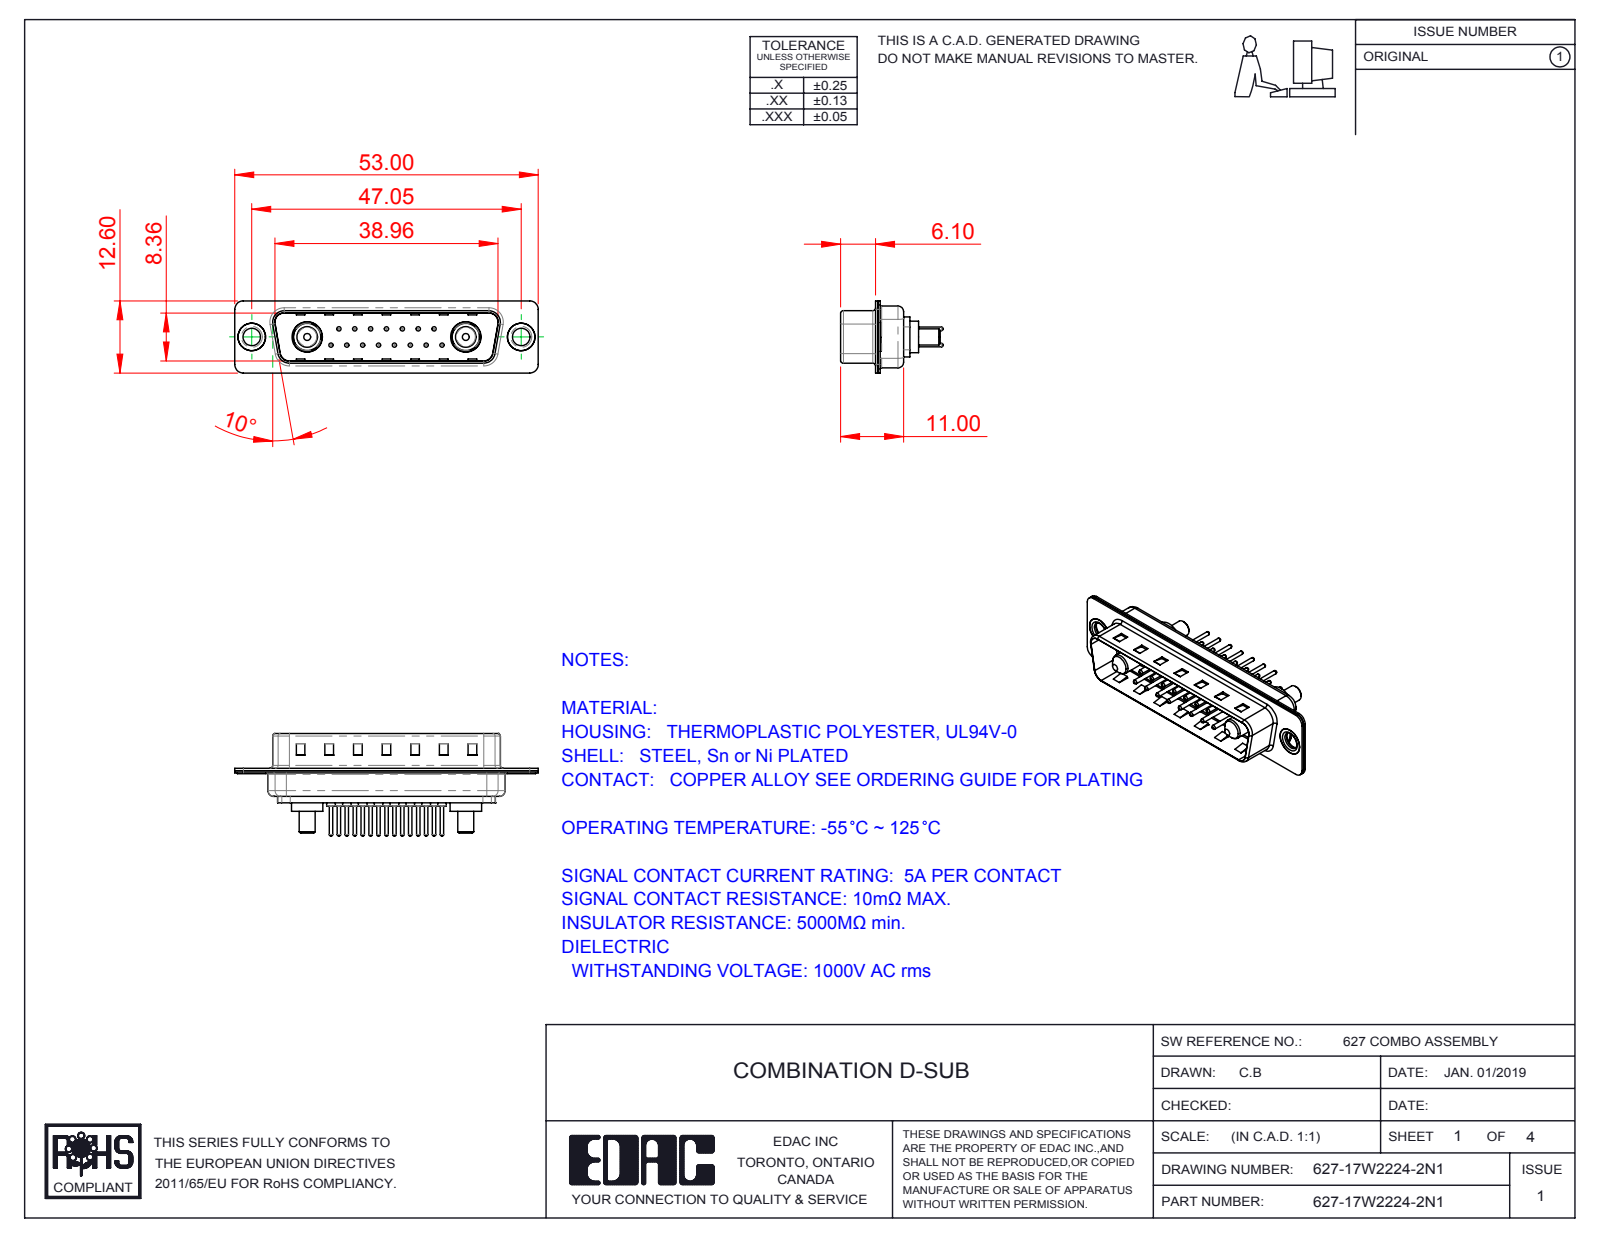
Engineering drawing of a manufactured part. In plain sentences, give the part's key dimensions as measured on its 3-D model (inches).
The part is named "627-17W2224-2N1; 627Combo Contact Row 1_24; 627Combo Housing_17W2; 627Combo Thru Hole Rivet (+4 more)". Its 3-D file was written by "SolidWorks 2016 (CONFIG_CONTROL_DESIGN)". It is 24 solids with 985 faces: 296 planar, 369 cylindrical and 320 other. Overall it measures 2.087 by 0.705 by 0.496 inches. Its volume is 0.17 cubic inches and its surface area 10.3 square inches. Round holes: 15 of diameter 0.03, 15 of diameter 0.063, 15 of diameter 0.079, 2 of diameter 0.12, 2 of diameter 0.157, 2 of diameter 0.189, 2 of diameter 0.191, 2 of diameter 0.209. Round bosses or shafts: 15 of diameter 0.059, 15 of diameter 0.024, 2 of diameter 0.217, 2 of diameter 0.205, 2 of diameter 0.197, 2 of diameter 0.193, 2 of diameter 0.187, 2 of diameter 0.148. Partial cylindrical surfaces (rounded edges, fillets, slot ends): 16 of radius 0.059, 12 of radius 0.079, 8 of radius 0.02, 8 of radius 0.063, 4 of radius 0.01, 4 of radius 0.024, 4 of radius 0.026, 4 of radius 0.035. The main face-to-face distances are 0.016, 0.032, 0.377, 0.345, 0.059, 0.22, 0.205, 0.031, 0.048, 0.393. The hole center spacings are 0.124, 0.109, 0.218, 0.327, 0.198, 0.295, 0.436, 0.198.
